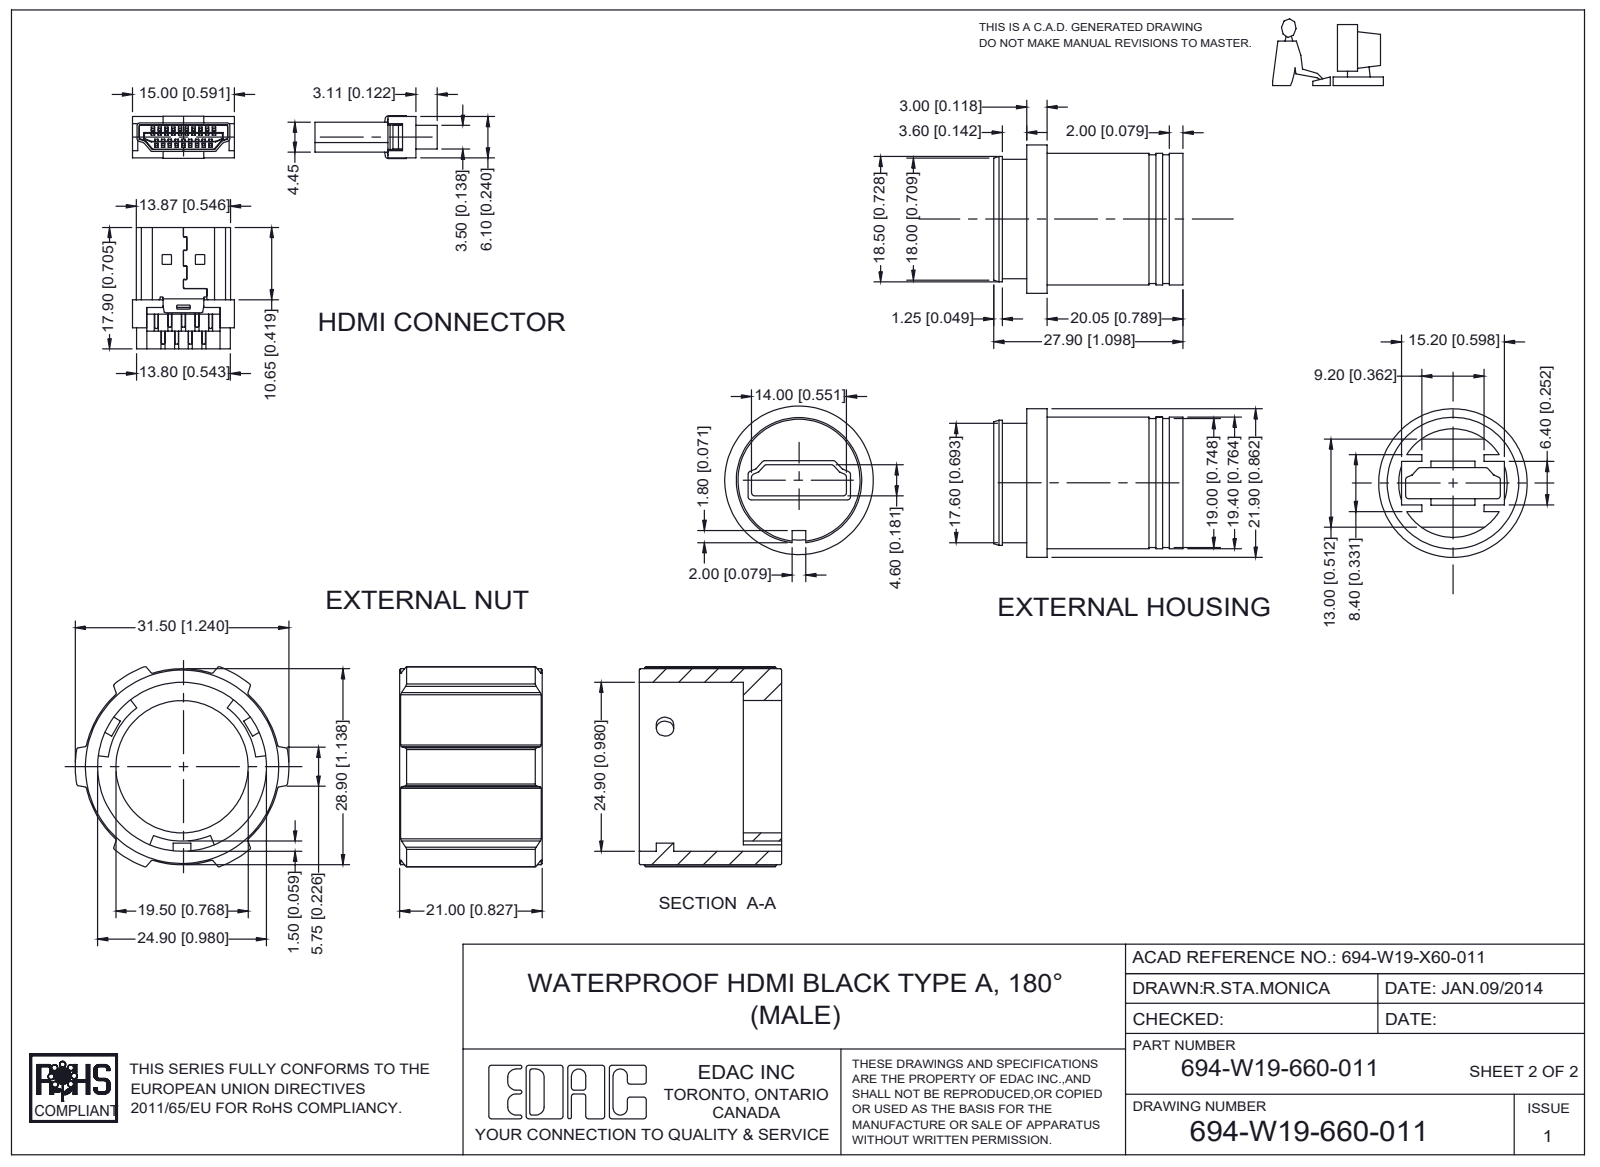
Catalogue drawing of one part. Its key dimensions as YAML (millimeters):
part_name: "HDMI HOUSING1 694-W19-X60-011; HDMI CONTACT3 694-W19-X60-011; HDMI CONTACT1 694-W19-X60-011; 694-W19-660-011 (+7 more)"
step_written_by: "SolidWorks 2020 (AUTOMOTIVE_DESIGN)"
units: millimeters
bodies: {solids: 25, faces: 2367, planar: 1591, cylindrical: 761, other: 15}
overall_size: [35.4, 31.5, 29.5]
volume: 9886
surface_area: 12696
round_holes:
  - {diameter: 15.94, count: 1}
  - {diameter: 17.1, count: 1}
  - {diameter: 19.5, count: 1}
  - {diameter: 24.9, count: 1}
round_bosses_or_shafts:
  - {diameter: 21.84, count: 1}
  - {diameter: 21.5, count: 1}
  - {diameter: 19.34, count: 1}
  - {diameter: 18.94, count: 1}
  - {diameter: 18.44, count: 1}
  - {diameter: 17.54, count: 1}
partial_cylinders:
  - {radius: 0.15, count: 284}
  - {radius: 0.11, count: 114}
  - {radius: 0.3, count: 29}
  - {radius: 0.5, count: 26}
  - {radius: 0.15, count: 19}
  - {radius: 0.2, count: 18}
  - {radius: 0.1, count: 10}
  - {radius: 0.17, count: 10}
face_to_face_distances: [0.4, 1, 3, 1.65, 8.65, 2.38, 5.65, 9.15, 7.4, 13.5]
